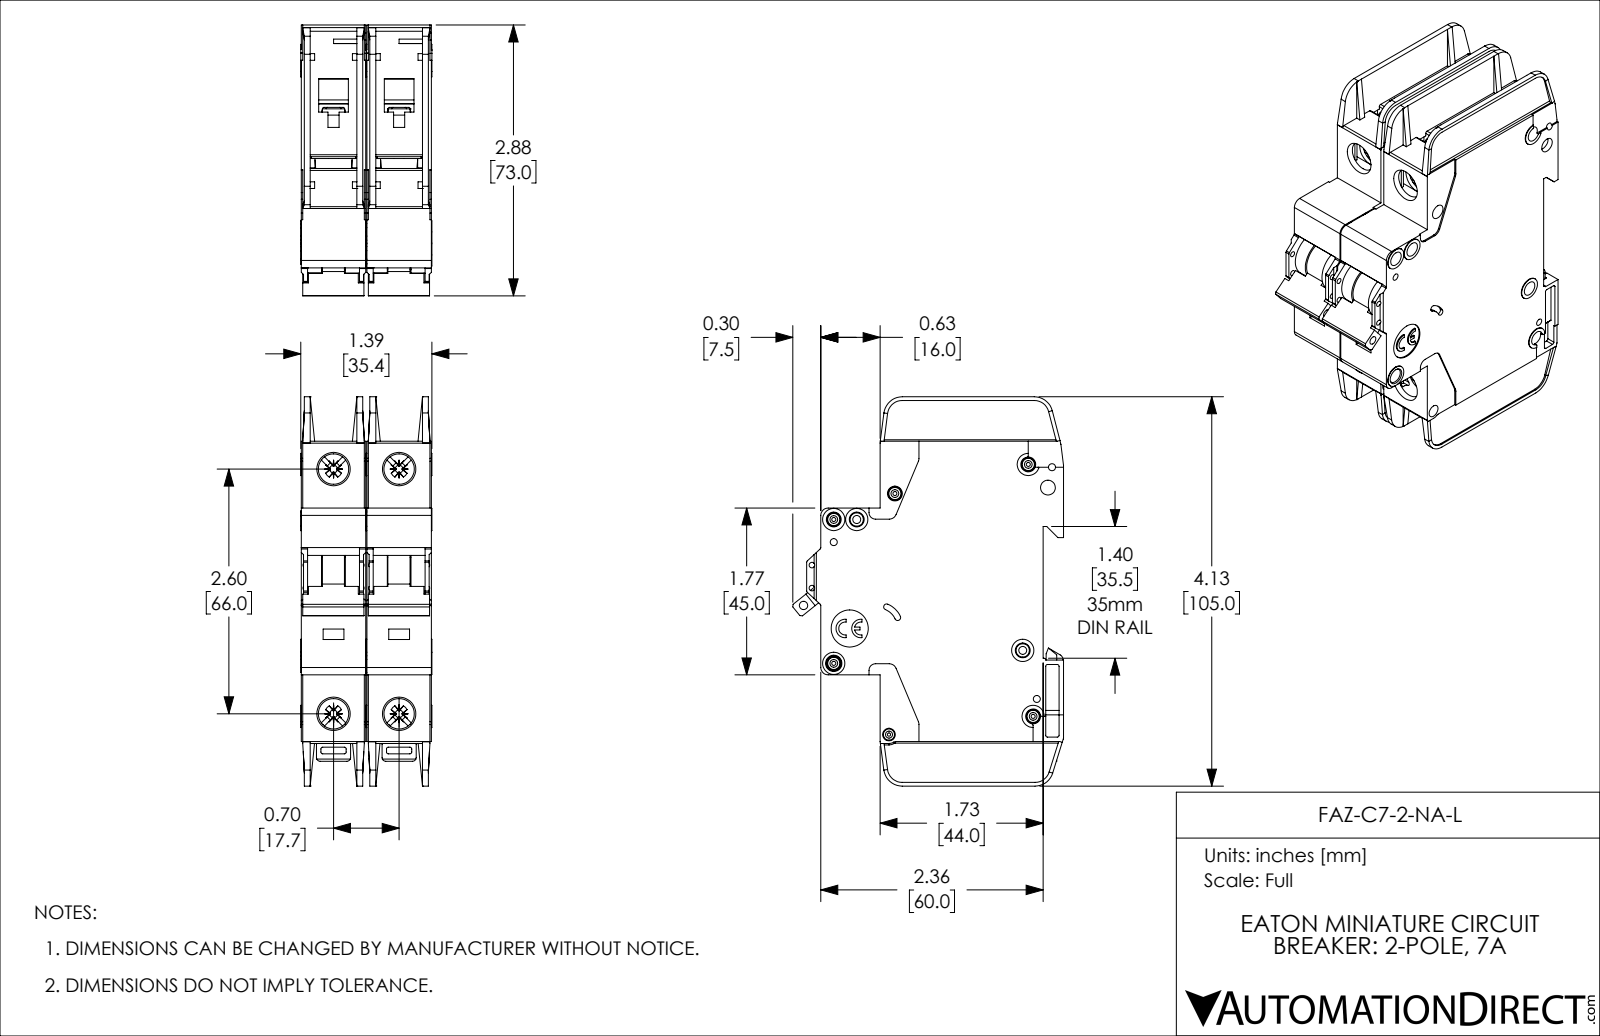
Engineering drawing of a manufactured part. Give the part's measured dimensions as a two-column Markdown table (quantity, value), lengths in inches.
| quantity | value |
| --- | --- |
| part name | FAZ-C7-2-NA-L |
| STEP written by | SolidWorks 2019 (AUTOMOTIVE_DESIGN) |
| units | inches |
| bodies | 2 solids, 2254 faces (1342 planar, 714 cylindrical, 198 other) |
| overall size | 4.134 × 2.876 × 1.394 |
| volume | 9.365 in³ |
| surface area | 82.01 in² |
| round holes (diameter × count) | 0.157 × 8, 0.043 × 5, 0.075 × 4, 0.323 × 4, 0.059 × 2, 0.085 × 2, 0.035 × 1, 0.089 × 1, 0.098 × 1, 0.134 × 1, 0.394 × 1 |
| round bosses / shafts (diameter × count) | 0.13 × 5, 0.236 × 4, 0.118 × 3, 0.098 × 2 |
| partial cylindrical surfaces (radius × count) | 0.02 × 57, 0.016 × 20, 0.039 × 14, 0.079 × 10, 0.043 × 8, 0.008 × 5, 0.197 × 5, 0.01 × 4 |
| main face-to-face distances | 0.697, 0.047, 0.685, 0.591, 0.094, 0.638, 0.543, 1.382, 0.744, 0.65 |
| hole center spacings | 0.244, 0.537, 0.697, 0.87, 2.598, 2.69, 0.189, 0.199 |
